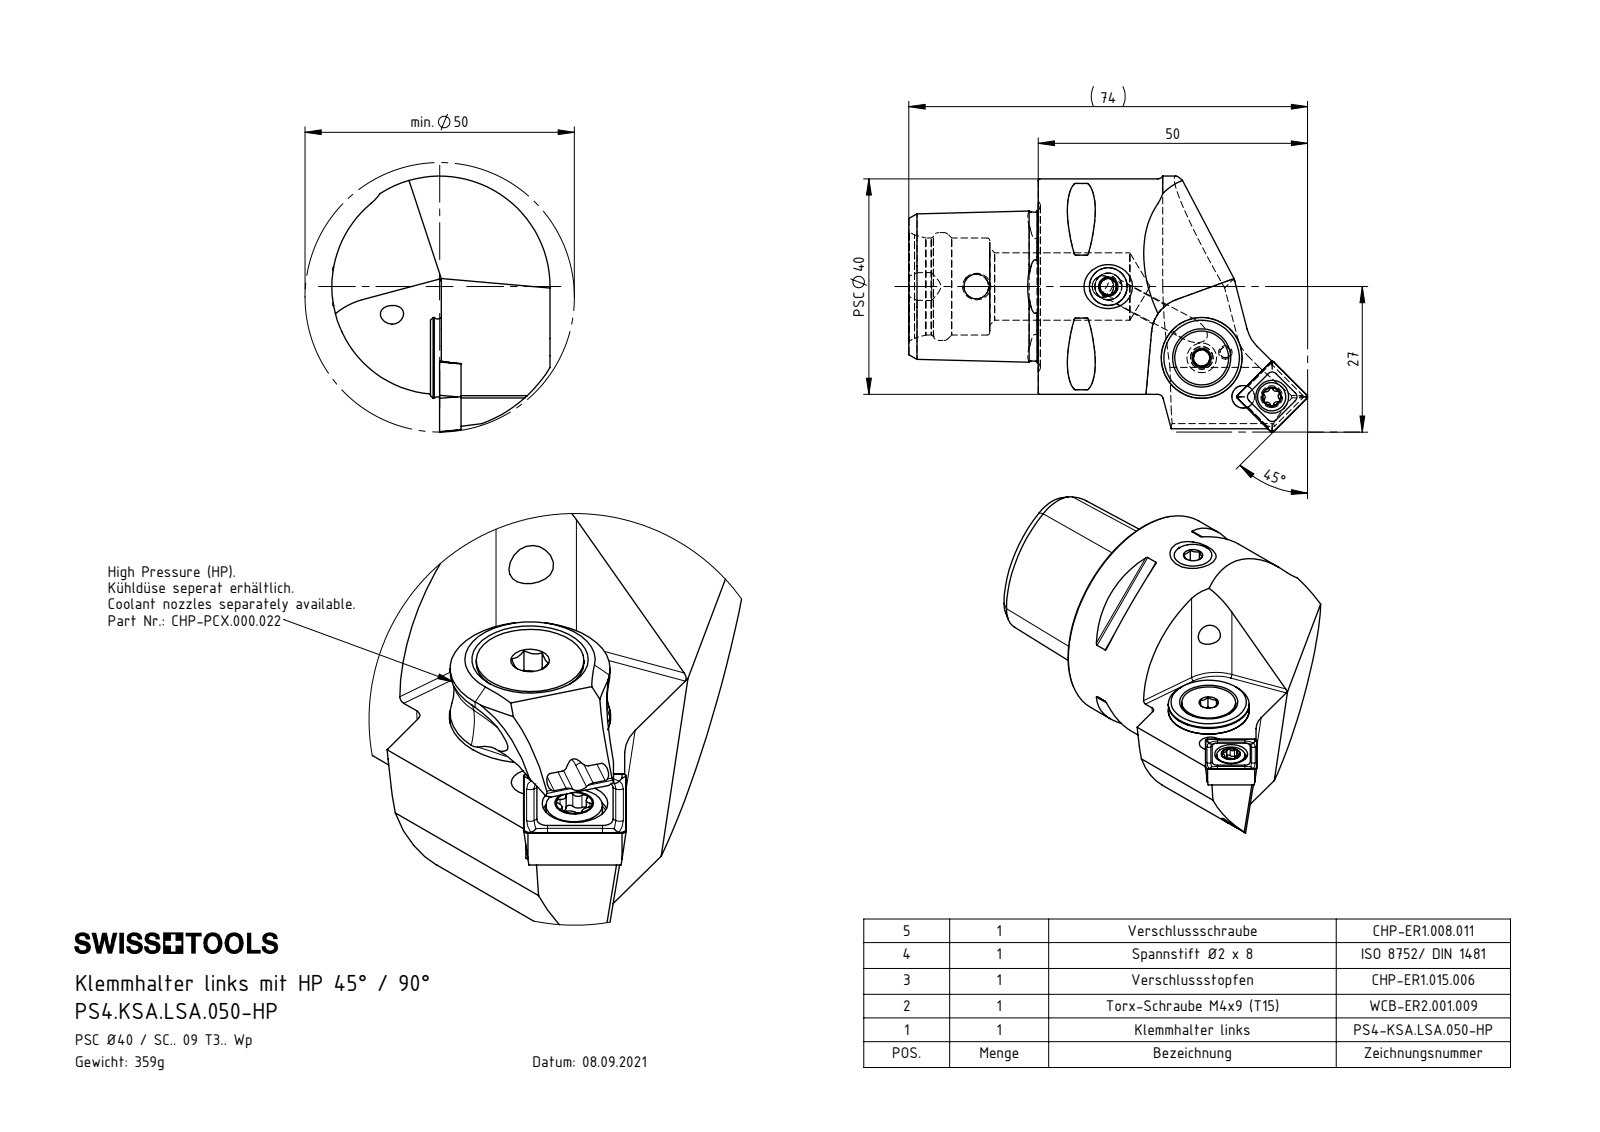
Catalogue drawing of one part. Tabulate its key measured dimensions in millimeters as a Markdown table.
| quantity | value |
| --- | --- |
| part name | DIN 3771 - 13x1; ISO 8752 2x8; CHP-ER1.008.011_A; PS4-KSA.LSA.050-HP_B (+7 more) |
| STEP written by | SolidWorks 2022 (AUTOMOTIVE_DESIGN) |
| units | millimeters |
| bodies | 9 solids, 377 faces (103 planar, 93 cylindrical, 181 other) |
| overall size | 74.01 × 47.5 × 40.5 |
| volume | 46 539 mm³ |
| surface area | 15 662 mm² |
| round holes (diameter × count) | 4.2 × 3, 3.3 × 2, 1.2 × 1, 2 × 1, 3 × 1, 4.4 × 1, 4.6 × 1, 5 × 1, 5.3 × 1, 6.1 × 1, 7 × 1, 10 × 1 |
| round bosses / shafts (diameter × count) | 40 × 1, 14.85 × 1, 13.4 × 1, 10 × 1, 8 × 1, 5.5 × 1, 5.25 × 1, 5 × 1 |
| partial cylindrical surfaces (radius × count) | 0.3 × 9, 1 × 7, 0.34 × 6, 0.59 × 6, 0.5 × 4, 6 × 3, 1.1 × 2, 1.2 × 2 |
| main face-to-face distances | 20.2, 24, 15.7, 4.5, 15.52, 1.5, 3, 16.53, 0.83, 3.67 |
| hole center spacings | 3.5, 4.5, 5.28, 5.39, 8.86, 10.55, 11.89, 11.97 |
